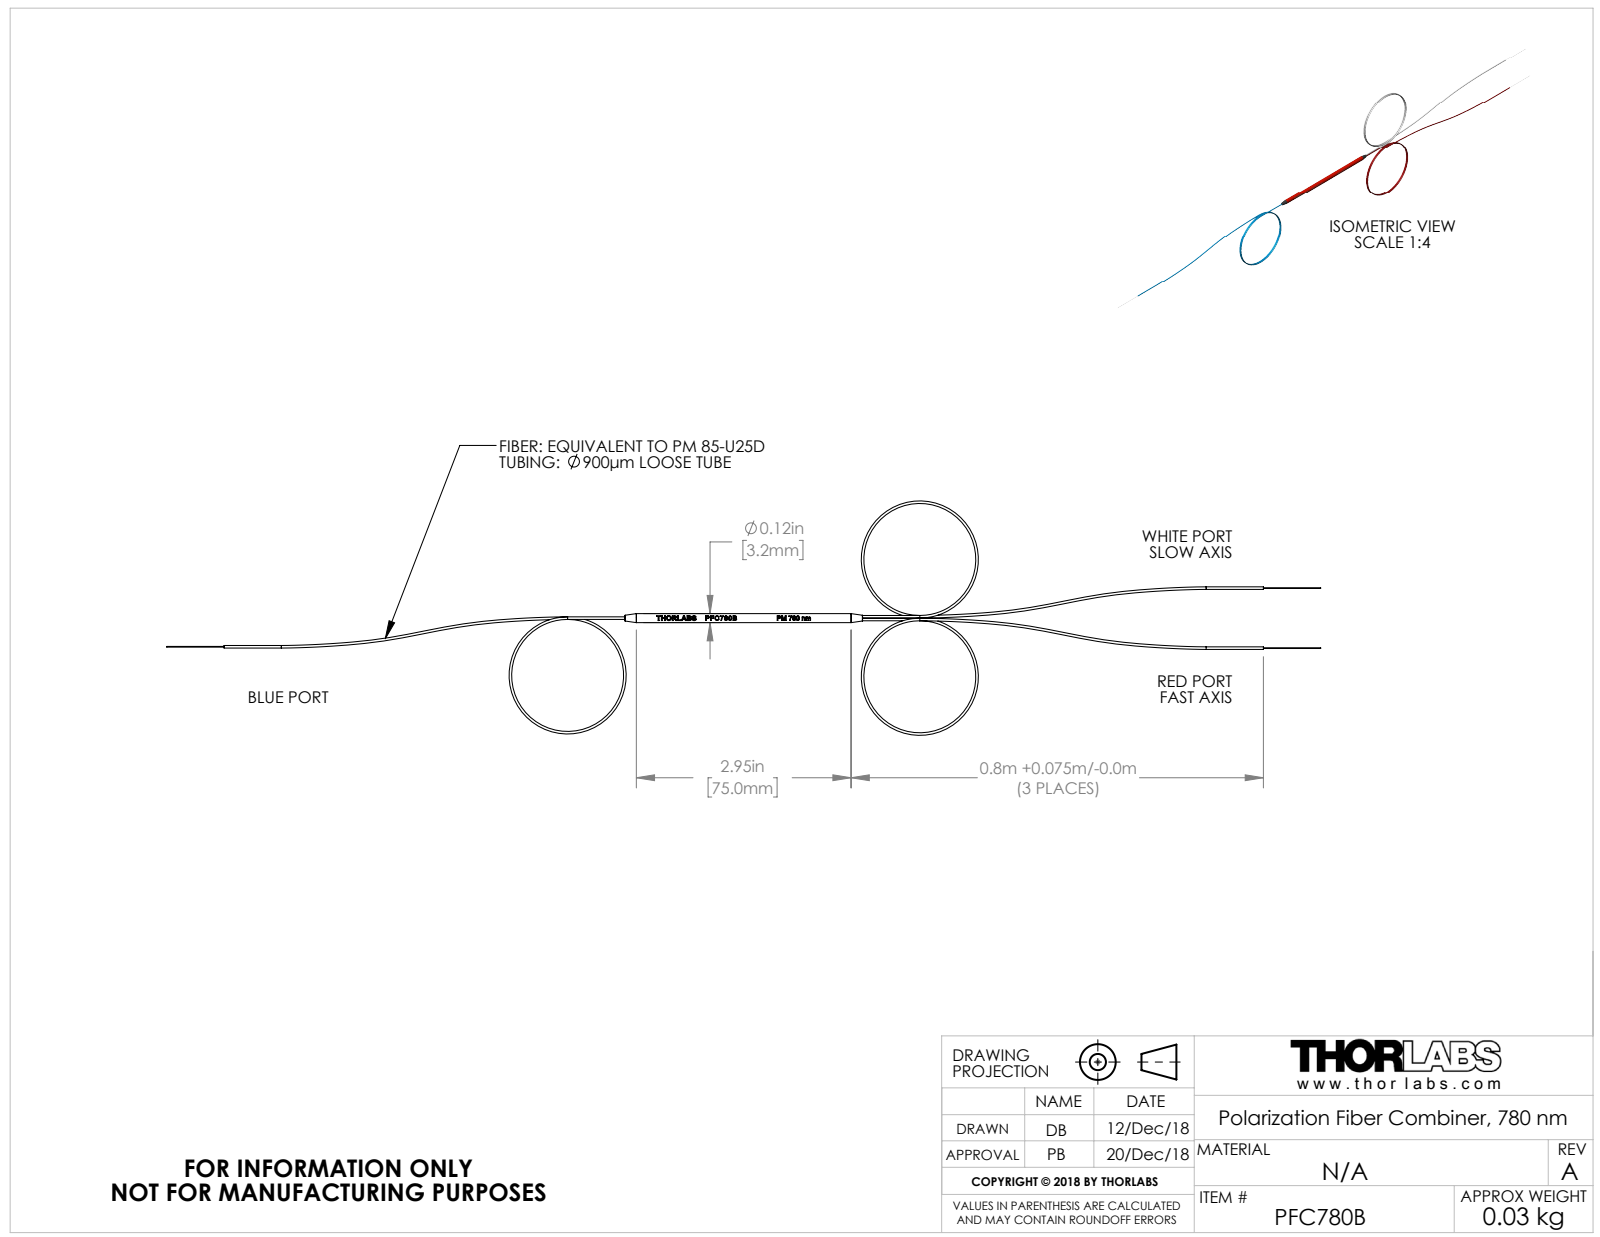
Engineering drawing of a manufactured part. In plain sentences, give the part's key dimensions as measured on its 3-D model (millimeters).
The part is named "DWG1631_75mm; LA000PLBTTW; LA000PLBTTB; TTN174132-E0W (+8 more)". Its 3-D file was written by "SolidWorks 2018 (CONFIG_CONTROL_DESIGN)". It is 14 solids with 255 faces: 41 planar, 154 cylindrical and 60 other. Overall it measures 403 by 81.85 by 5.1 millimeters. Its volume is 833 cubic millimeters and its surface area 7 381 square millimeters. Round holes: 6 of diameter 0.5, 3 of diameter 0.95, 1 of diameter 2.69. Round bosses or shafts: 6 of diameter 0.9, 5 of diameter 0.25, 1 of diameter 3.15, 1 of diameter 2.5. Partial cylindrical surfaces (rounded edges, fillets, slot ends): 2 of radius 0.45, 1 of radius 1. The main face-to-face distances are 3, 69, 72, 6, 66, 75, 63, 58.5, 52.5, 16.5. The hole center spacings are 10.2, 0.47, 0.48, 0.95, 4.03, 9.74, 10.24, 10.66.
